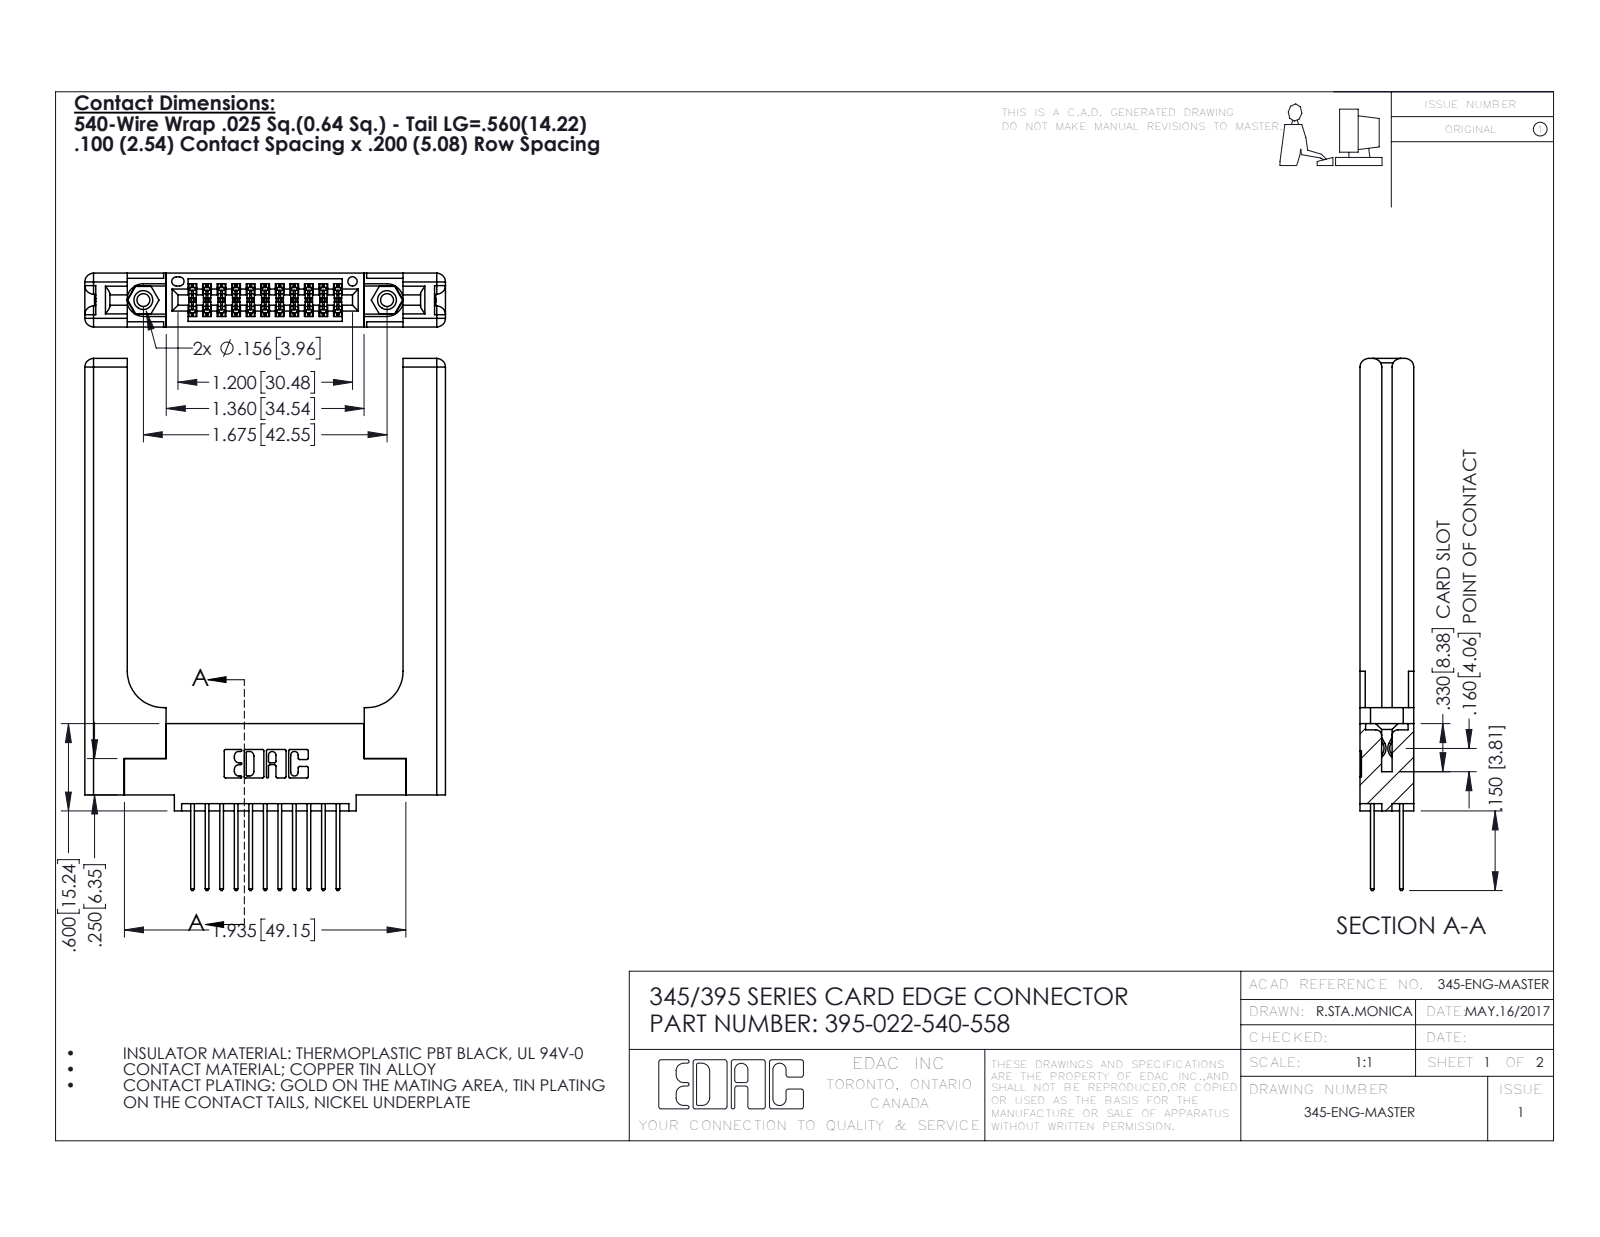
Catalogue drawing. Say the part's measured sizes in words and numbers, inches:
The part is named "345 Part_0.110 Offset - 0.156 Dia-TH; 345-292-001_345-293-140; 395-022-540-558; 345-220-058_345-220-058 (+1 more)". Its 3-D file was written by "SolidWorks 2016 (CONFIG_CONTROL_DESIGN)". It is 27 solids with 1486 faces: 958 planar, 468 cylindrical and 60 other. Overall it measures 3.657 by 2.479 by 0.37 inches. Its volume is 0.873 cubic inches and its surface area 21.03 square inches. Round holes: 2 of diameter 0.089, 2 of diameter 0.125, 2 of diameter 0.156, 1 of diameter 0.064. Round bosses or shafts: 2 of diameter 0.155. Partial cylindrical surfaces (rounded edges, fillets, slot ends): 33 of radius 0.006, 22 of radius 0.01, 22 of radius 0.01, 16 of radius 0.06, 6 of radius 0.007, 6 of radius 0.031, 3 of radius 0.026, 2 of radius 0.014. The main face-to-face distances are 0.37, 0.072, 0.298, 0.148, 0.15, 0.077, 0.22, 0.2, 0.098, 0.272. The hole center spacings are 0.27, 1.443, 1.675.
